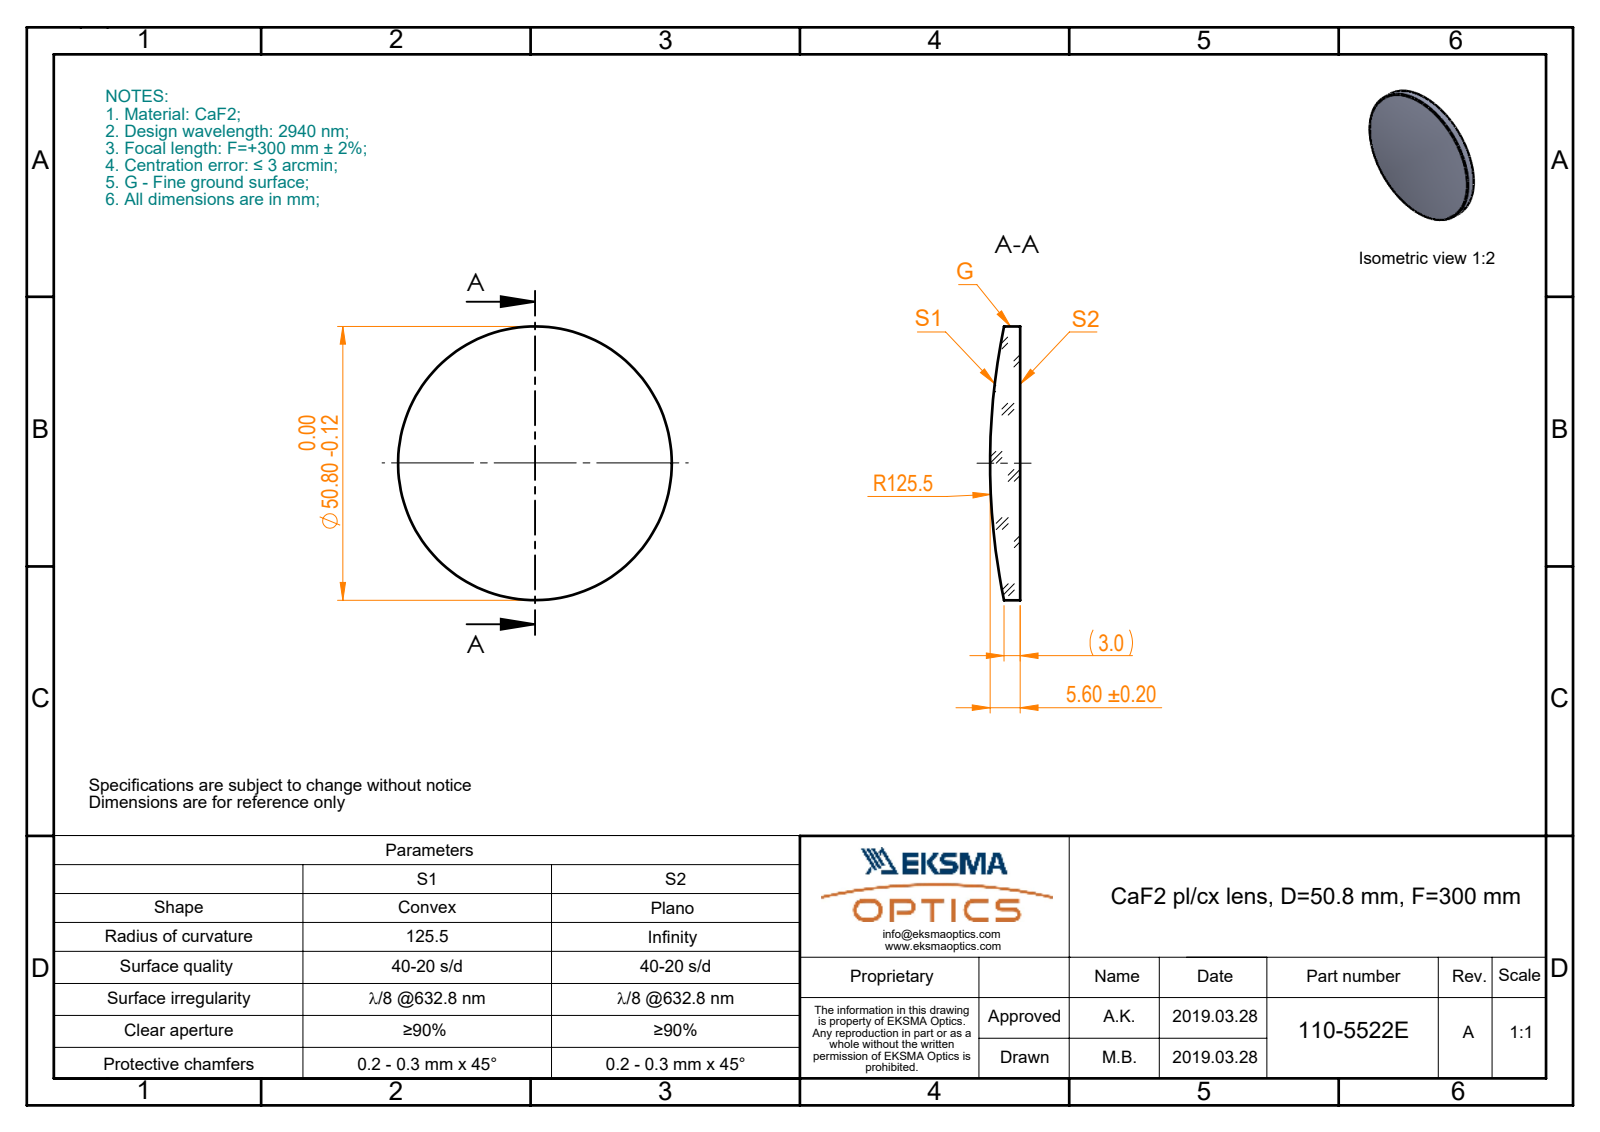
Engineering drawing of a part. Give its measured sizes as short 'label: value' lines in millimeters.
name: 110-5522E CaF2 pl-cx 50.8 F300
written by: SolidWorks 2017 (CONFIG_CONTROL_DESIGN)
unit: mm
bodies: 1 solid, 5 faces (1 planar, 2 cylindrical, 2 other)
size: 50.8 × 50.8 × 5.6
volume: 8 727 mm³; area: 4 554 mm²
bosses: 1× ⌀50.8
